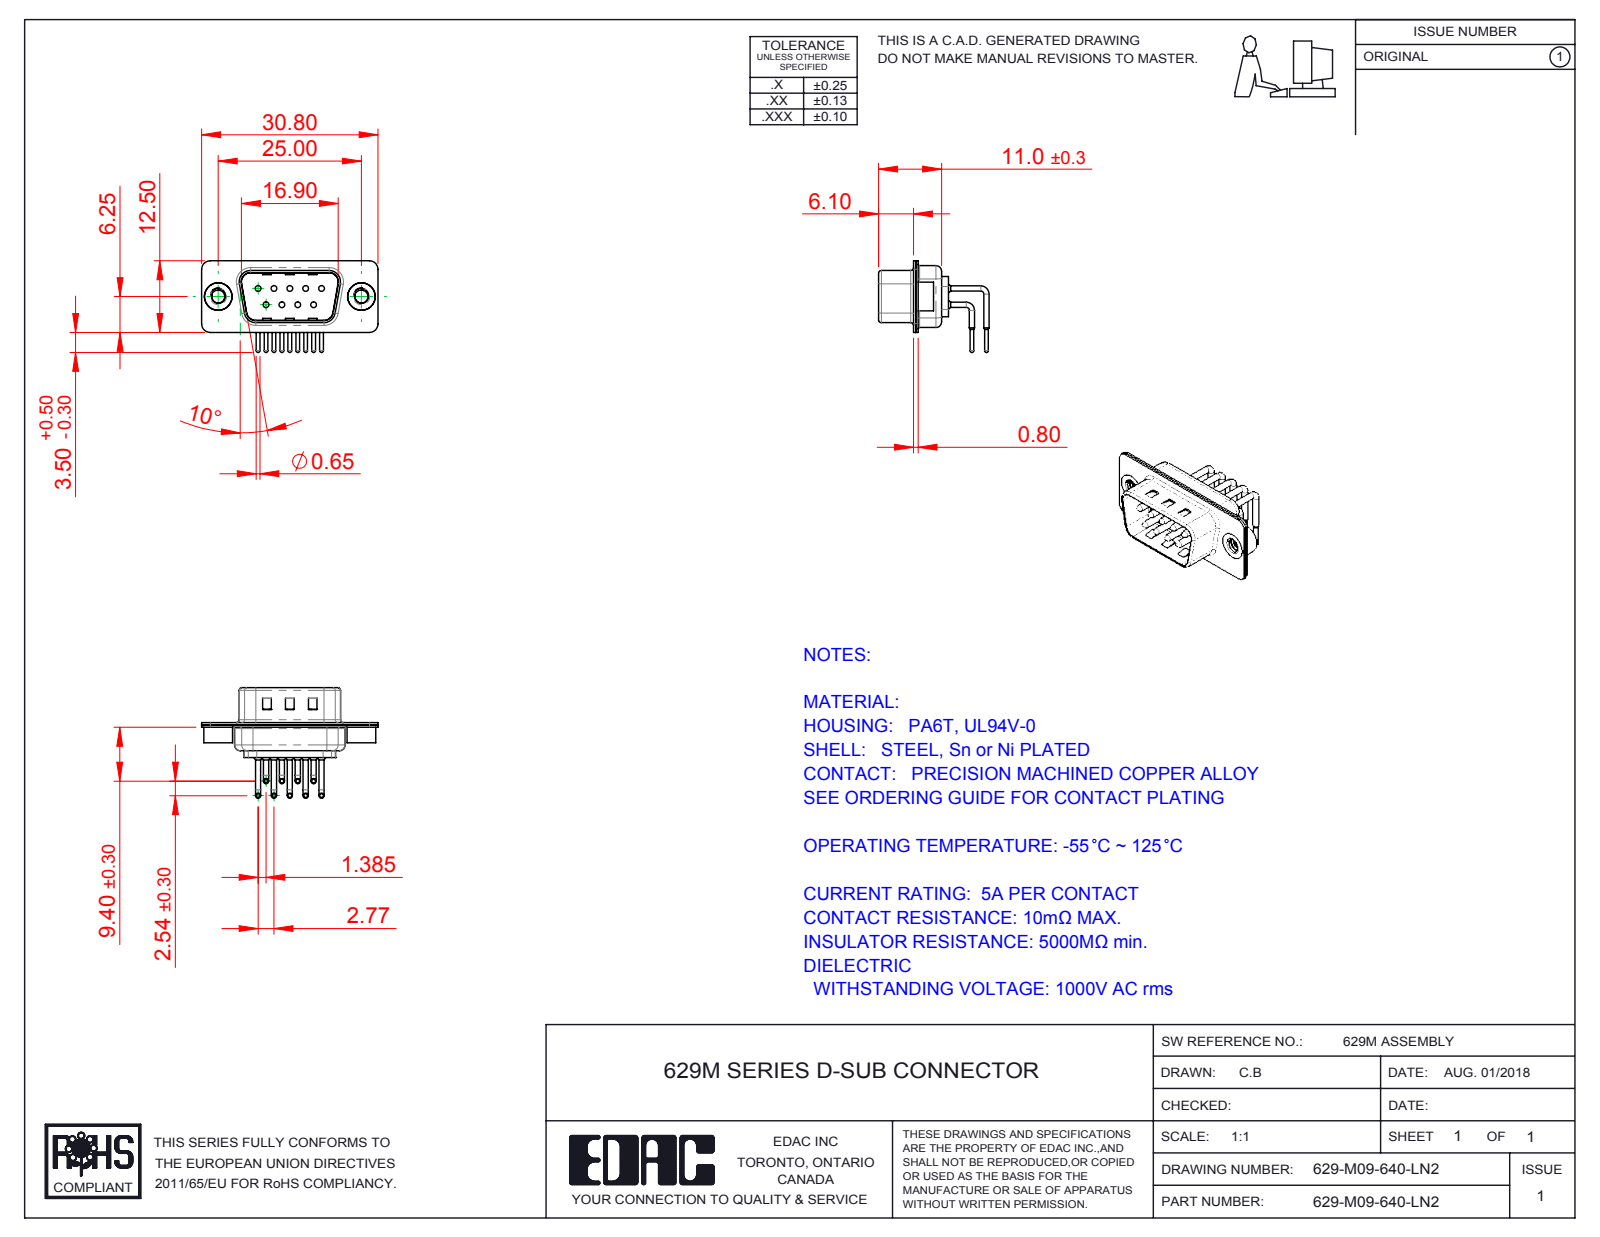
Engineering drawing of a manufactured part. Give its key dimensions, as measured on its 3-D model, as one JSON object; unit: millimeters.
{"part_name": "629M Contact Row 2; 629M Contact Row 1; 629M Shell Rear_09 Contacts; 629M Shell Front_09 Contacts (+3 more)", "step_written_by": "SolidWorks 2016 (CONFIG_CONTROL_DESIGN)", "units": "millimeters", "bodies": {"solids": 14, "faces": 1294, "planar": 683, "cylindrical": 453, "other": 158}, "overall_size": [30.8, 19.29, 16], "volume_mm3": 1381, "surface_area_mm2": 3912, "round_holes": [[1, 9], [1.7, 9], [2, 9], [2.26, 2], [4, 2], [4.8, 2]], "round_bosses_or_shafts": [[0.9, 18], [1.5, 9], [0.65, 9], [5, 2], [4.9, 2]], "partial_cylinders_radius": [[1.5, 16], [2, 12], [1.01, 9], [0.5, 8], [1.6, 8], [0.25, 4], [0.6, 4], [0.65, 4]], "face_to_face_distances": [0.4, 0.85, 0.8, 9.55, 1.25, 10.4, 8.7, 0.35, 6.1, 5.7], "hole_center_spacings": [3.16, 2.77, 5.54, 5.03, 5.04, 8.31, 7.1, 7.48]}
